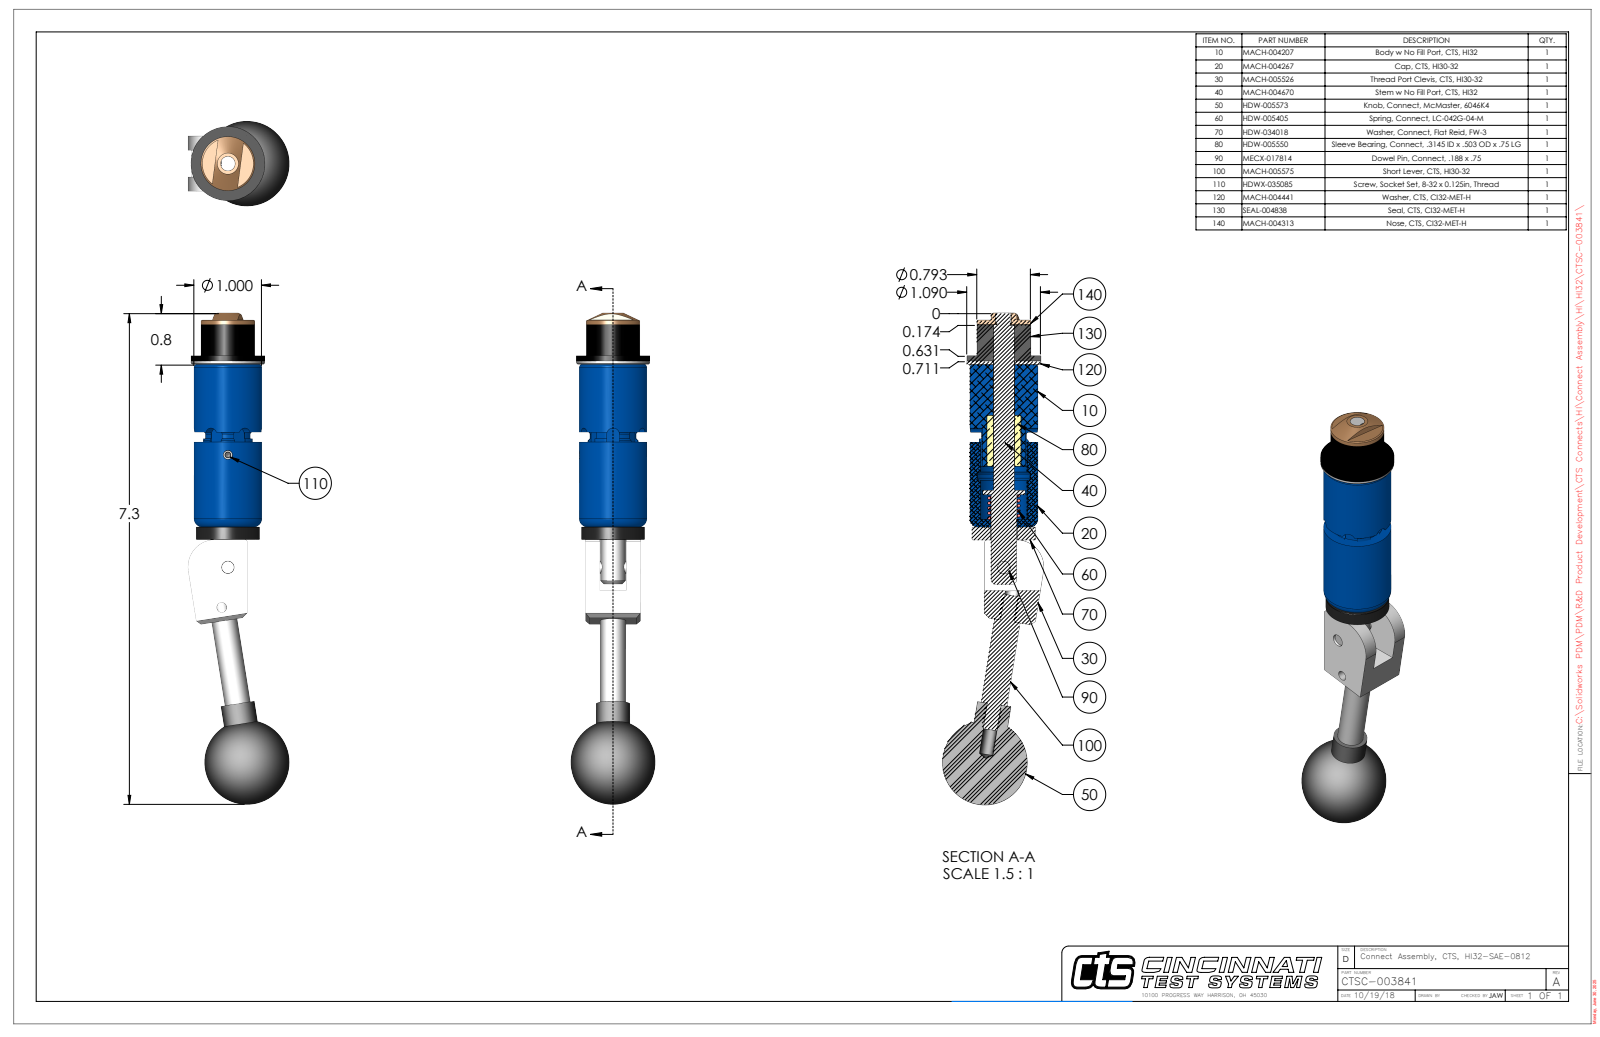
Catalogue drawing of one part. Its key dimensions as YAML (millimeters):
part_name: "CTSC-003841"
step_written_by: "SolidWorks 2023 (AUTOMOTIVE_DESIGN)"
units: millimeters
bodies: {solids: 9, faces: 268, planar: 100, cylindrical: 110, other: 58}
overall_size: [184.3, 37.9, 31.8]
volume: 67830
surface_area: 22970
round_holes:
  - {diameter: 5.1, count: 2}
  - {diameter: 3.5, count: 1}
  - {diameter: 3.8, count: 1}
  - {diameter: 4.8, count: 1}
  - {diameter: 5.4, count: 1}
  - {diameter: 7.9, count: 1}
  - {diameter: 8, count: 1}
  - {diameter: 8, count: 1}
  - {diameter: 9.8, count: 1}
  - {diameter: 10, count: 1}
  - {diameter: 17.5, count: 1}
round_bosses_or_shafts:
  - {diameter: 6.4, count: 2}
  - {diameter: 5.1, count: 2}
  - {diameter: 27.7, count: 1}
  - {diameter: 25.4, count: 1}
  - {diameter: 23.8, count: 1}
  - {diameter: 20.1, count: 1}
  - {diameter: 12.7, count: 1}
  - {diameter: 9.7, count: 1}
partial_cylinders:
  - {radius: 2.4, count: 6}
  - {radius: 0.7, count: 2}
  - {radius: 9.5, count: 1}
  - {radius: 10.2, count: 1}
  - {radius: 11.8, count: 1}
face_to_face_distances: [1.3, 5.3, 15.3, 13.6, 14.9, 75.8, 62.2, 60.9, 20.6, 80.6]
hole_center_spacings: [15.2, 42.1, 57.2]
